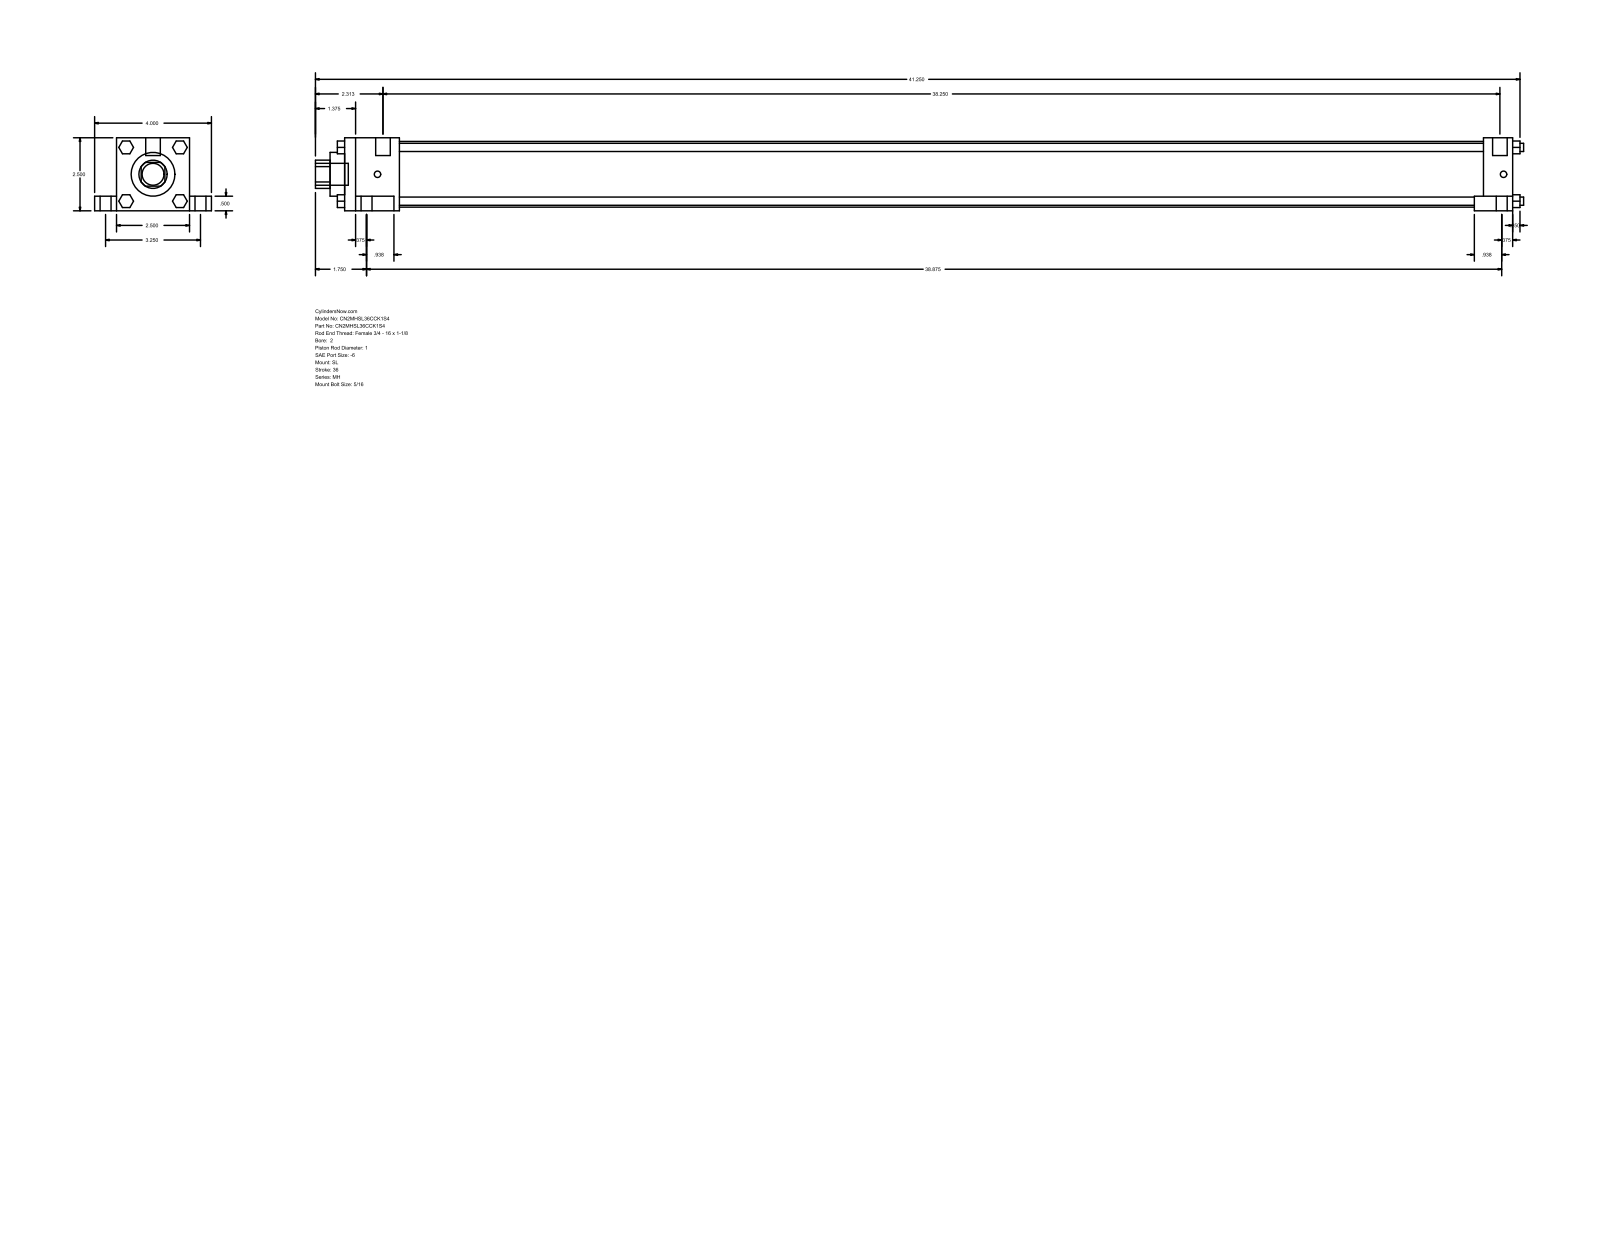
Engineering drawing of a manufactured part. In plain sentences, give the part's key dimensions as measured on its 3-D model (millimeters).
The part is named "MH_SL__0200_1". Its 3-D file was written by "GSSL Pune (CONFIG_CONTROL_DESIGN)". It is 0 solids with 148 faces: 112 planar, 36 cylindrical and 0 other. Overall it measures 1050.92 by 101.6 by 63.5 millimeters. Round holes: 1 of diameter 25.4, 1 of diameter 38.1, 1 of diameter 57.15. Round bosses or shafts: 4 of diameter 15.88, 4 of diameter 9.53, 4 of diameter 7.14, 4 of diameter 5.56, 2 of diameter 12.7, 1 of diameter 19.05. Partial cylindrical surfaces (rounded edges, fillets, slot ends): 1 of radius 12.29. The main face-to-face distances are 63.5, 1016, 12.7, 19.05, 50.8, 82.55, 9.52, 25.4, 990.6, 47.63.
